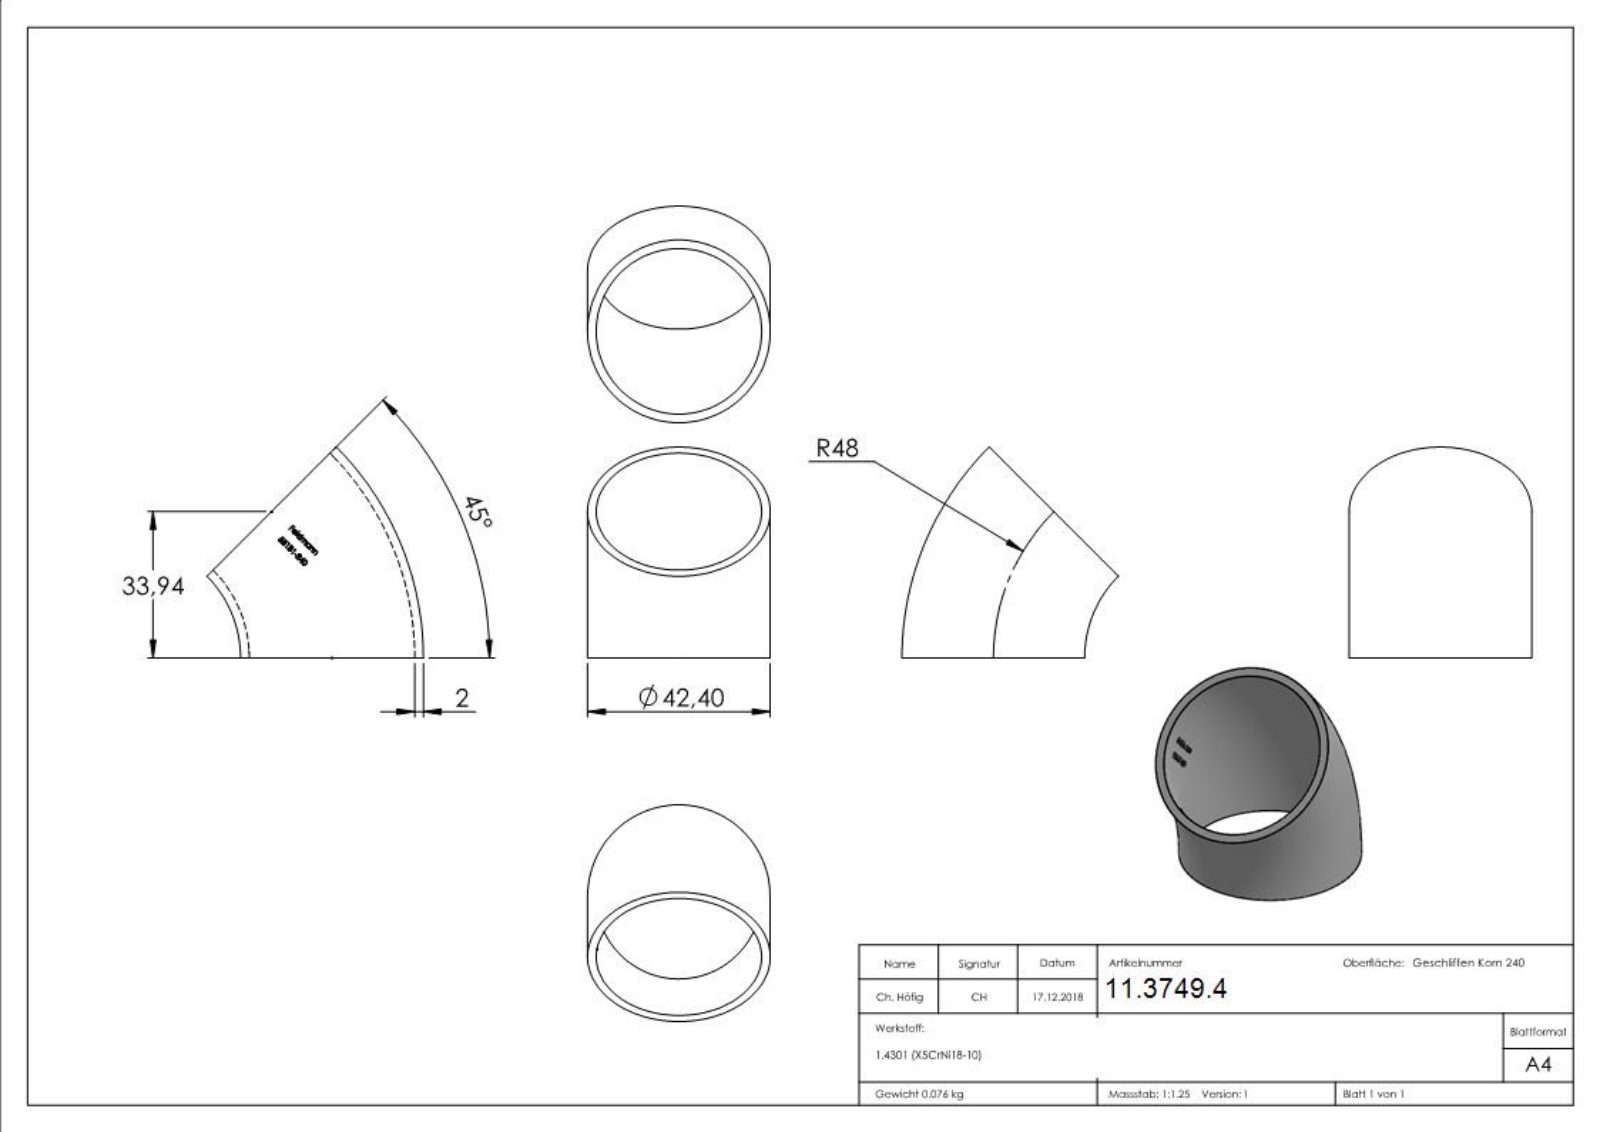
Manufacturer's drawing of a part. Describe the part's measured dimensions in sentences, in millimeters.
The part is named "55181-240". Its 3-D file was written by "SolidWorks 2015 (CONFIG_CONTROL_DESIGN)". It is 1 solid with 227 faces: 103 planar, 0 cylindrical and 124 other. Overall it measures 50.25 by 48.93 by 42.4 millimeters. Its volume is 9 569 cubic millimeters and its surface area 10 087 square millimeters. The main face-to-face distances are 4.45, 2.85, 2.97, 0.54, 3.38, 4.32, 2.04, 1.18, 1, 2.41.
